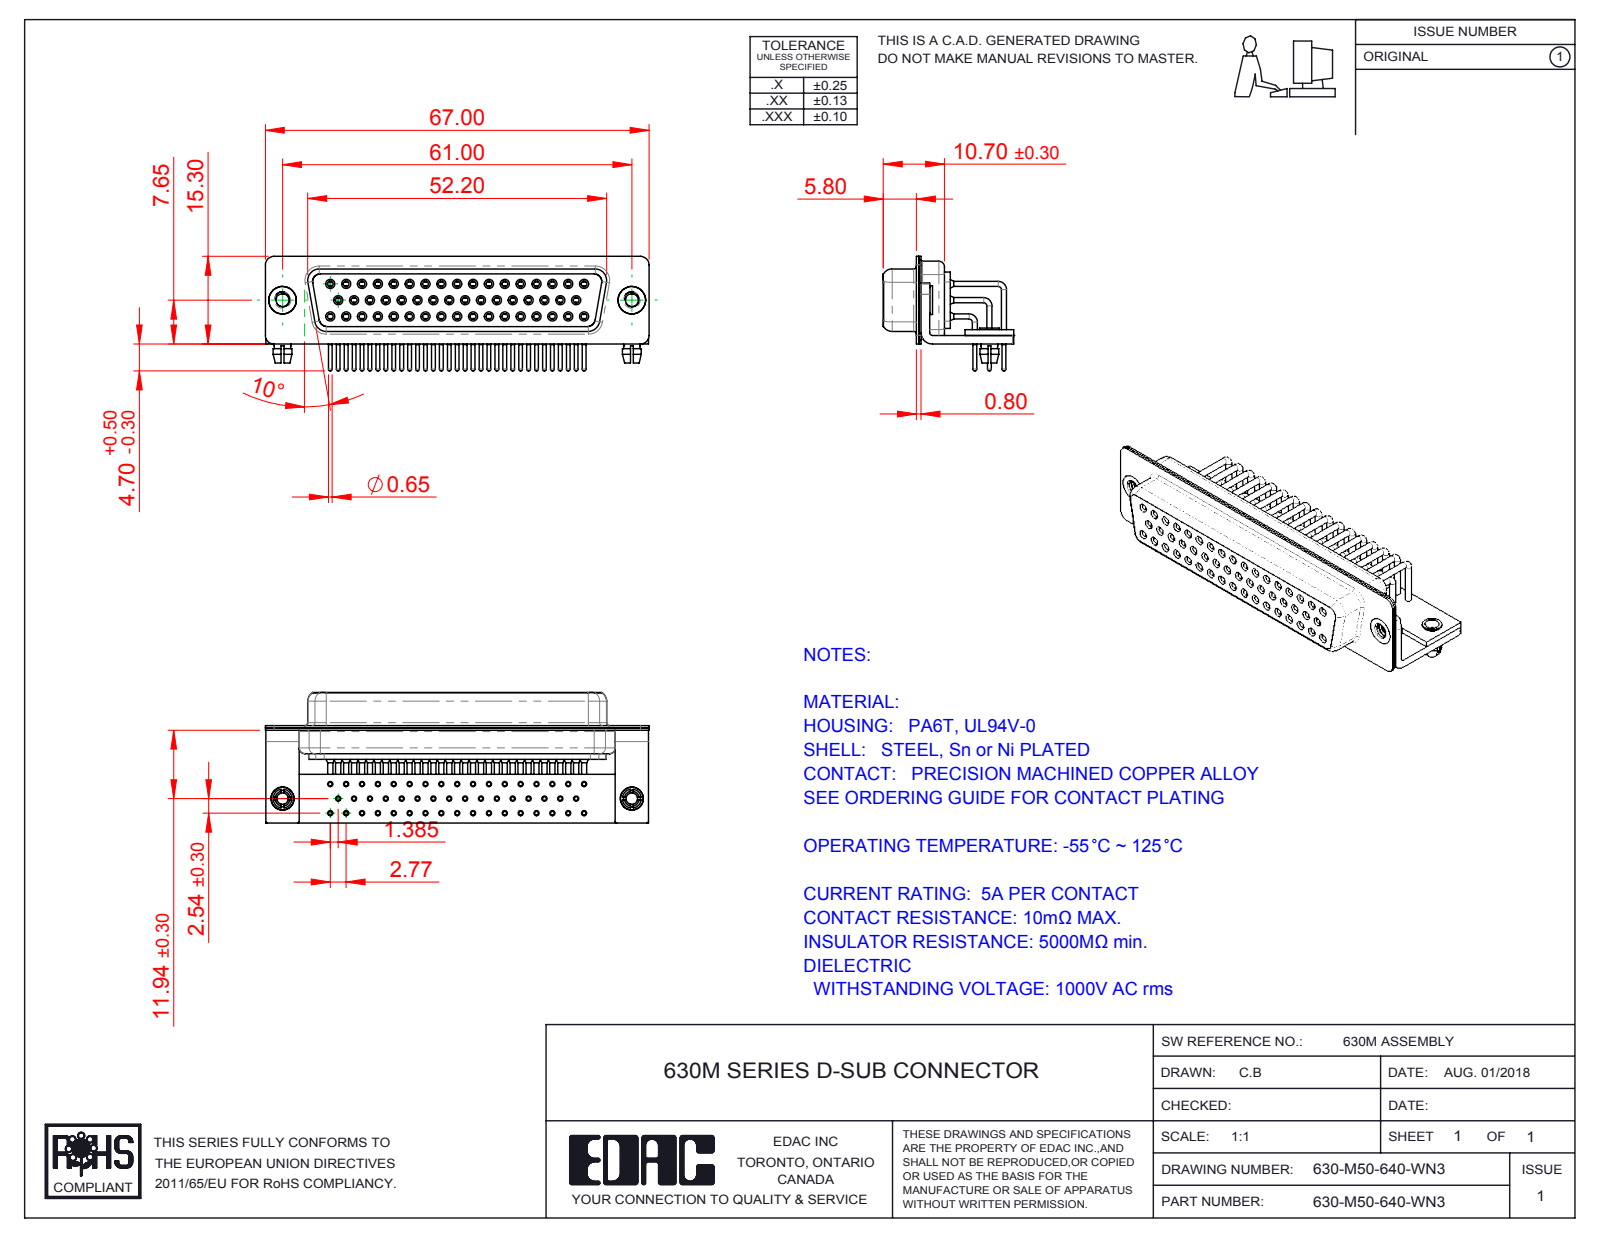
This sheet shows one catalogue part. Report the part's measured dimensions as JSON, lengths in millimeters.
{"part_name": "630M Shell Front_50 Contacts; 630M Shell Rear_50 Contacts; 630M Contact Row 1_50 Contacts; 630M Contact Row 3 (+7 more)", "step_written_by": "SolidWorks 2016 (CONFIG_CONTROL_DESIGN)", "units": "millimeters", "bodies": {"solids": 60, "faces": 3171, "planar": 891, "cylindrical": 1441, "other": 839}, "overall_size": [67, 22.8, 20], "volume_mm3": 7910, "surface_area_mm2": 18844, "round_holes": [[2, 52], [0.9, 50], [1, 50], [1.1, 50], [1.7, 50], [1.8, 50], [2.26, 2], [2.5, 2], [3.2, 2], [4, 2], [4.8, 2]], "round_bosses_or_shafts": [[0.9, 59], [1.6, 50], [1.5, 50], [0.65, 50], [5, 2], [4.9, 2], [4, 2], [3.4, 2]], "partial_cylinders_radius": [[0.25, 16], [1.5, 16], [2, 13], [1.35, 8], [1.6, 8], [0.5, 5], [0.6, 4], [0.65, 4]], "face_to_face_distances": [0.4, 1, 2.2, 0.85, 1.35, 11.85, 12.25, 5.8, 5.9, 0.8], "hole_center_spacings": [2.77, 5.54, 8.31, 11.08, 13.85, 16.62, 3.16, 19.39]}
